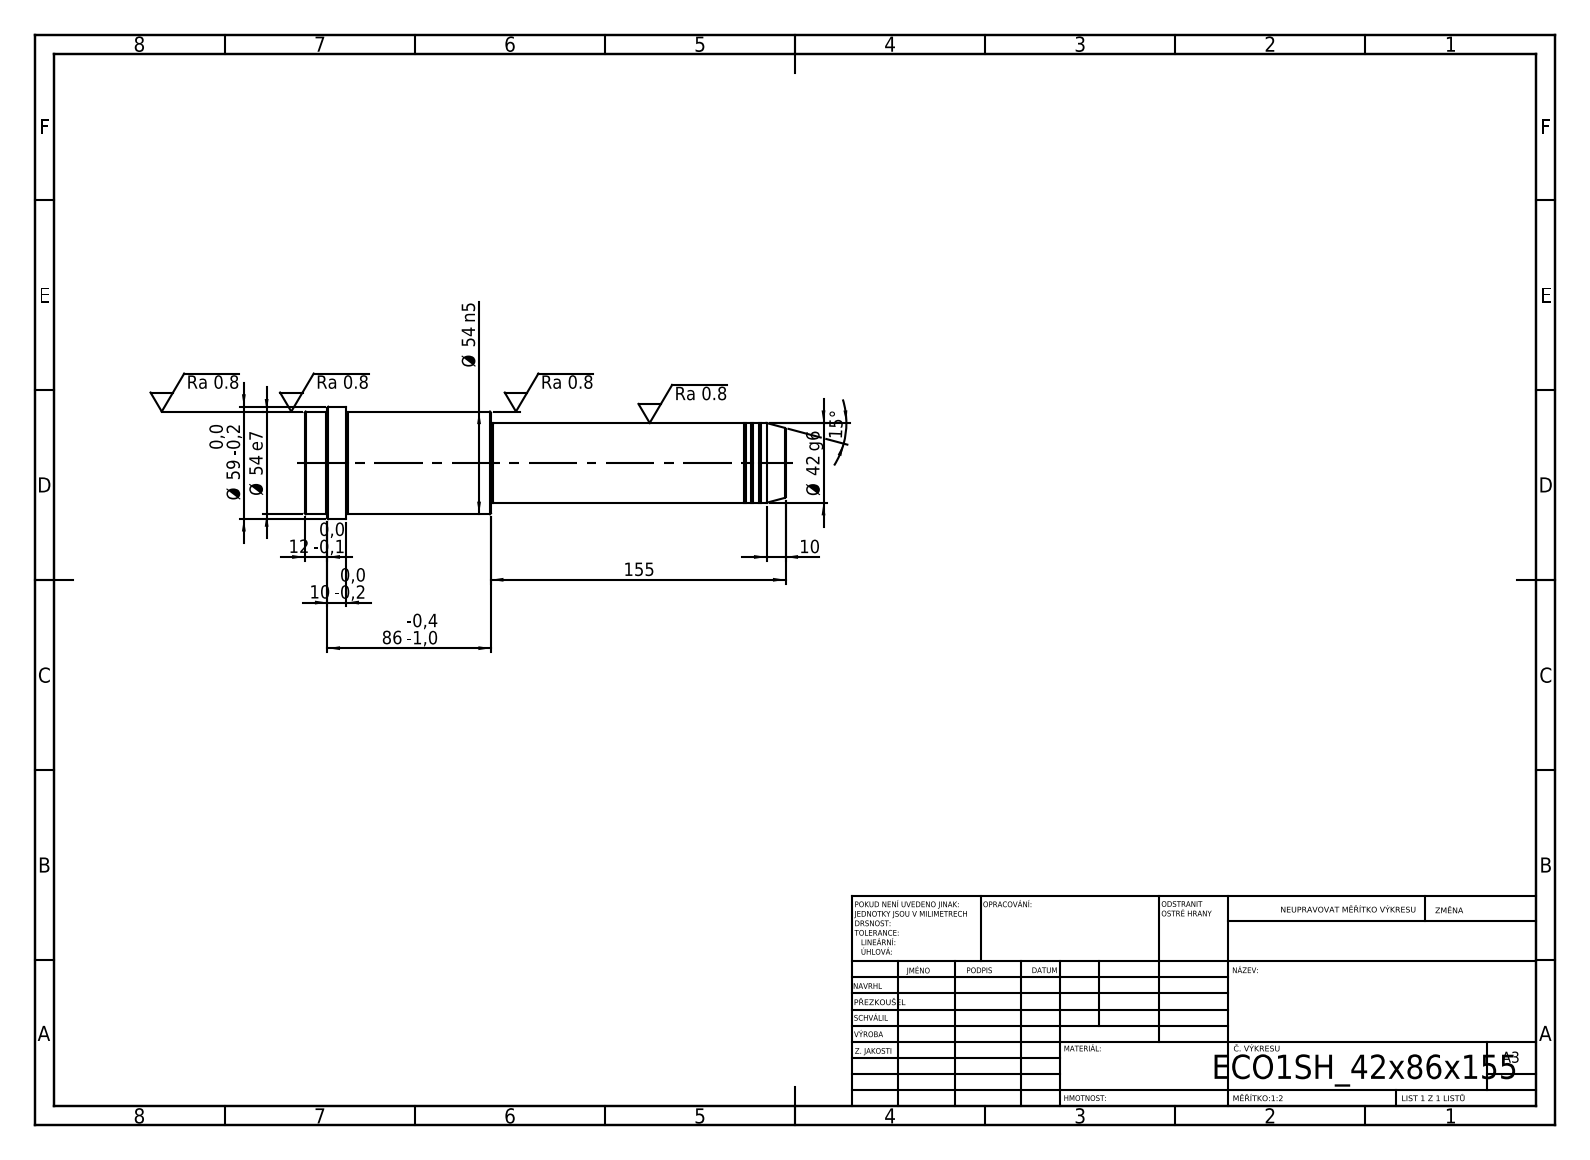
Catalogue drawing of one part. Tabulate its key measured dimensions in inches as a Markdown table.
| quantity | value |
| --- | --- |
| STEP written by | SolidWorks 2019 (CONFIG_CONTROL_DESIGN) |
| units | inches |
| bodies | 1 solid, 52 faces (6 planar, 16 cylindrical, 30 other) |
| overall size | 9.961 × 2.323 × 2.323 |
| volume | 26.94 in³ |
| surface area | 66.18 in² |
| round bosses / shafts (diameter × count) | 2.323 × 1, 2.126 × 1, 1.654 × 1, 1.614 × 1 |
| main face-to-face distances | 9.961, 6.102, 3.858, 9.094, 2.992, 0.866, 9.488, 3.386, 0.394, 0.472 |
